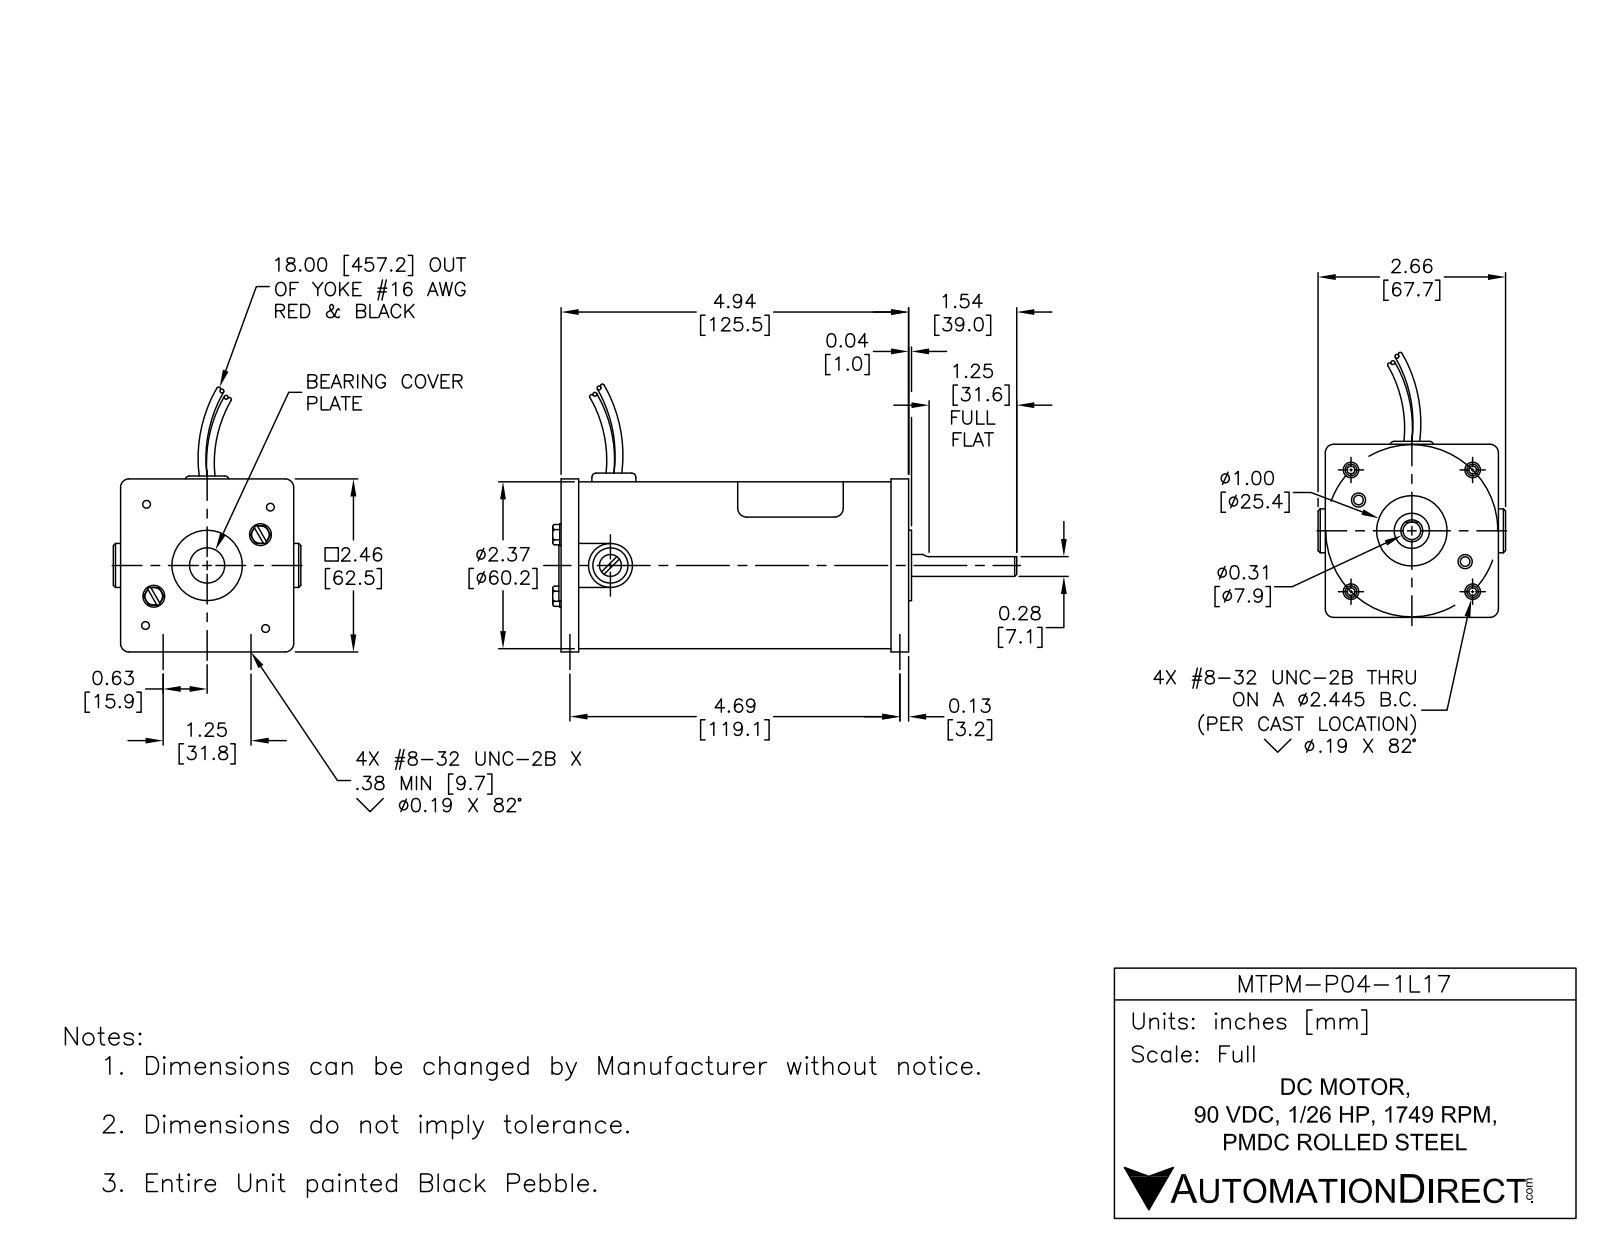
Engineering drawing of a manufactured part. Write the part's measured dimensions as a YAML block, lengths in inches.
part_name: "MTPM-P04-1L17"
step_written_by: "SolidWorks 2013 (AUTOMOTIVE_DESIGN)"
units: inches
bodies: {solids: 20, faces: 150, planar: 71, cylindrical: 76, other: 3}
overall_size: [6.604, 3.71, 2.602]
volume: 5.787
surface_area: 111.7
round_holes:
  - {diameter: 0.063, count: 4}
  - {diameter: 0.156, count: 2}
  - {diameter: 0.25, count: 1}
  - {diameter: 0.562, count: 1}
  - {diameter: 1, count: 1}
  - {diameter: 2.25, count: 1}
round_bosses_or_shafts:
  - {diameter: 0.312, count: 4}
  - {diameter: 0.1, count: 2}
  - {diameter: 2.375, count: 1}
  - {diameter: 0.625, count: 1}
  - {diameter: 0.625, count: 1}
face_to_face_distances: [0.25, 4.694, 4.444, 4.944, 2.46, 4.981, 4.731, 0.287, 0.037, 0.25]
hole_center_spacings: [1.223, 1.729, 0.44, 0.875, 1.306, 1.678, 2.08, 2.445]
